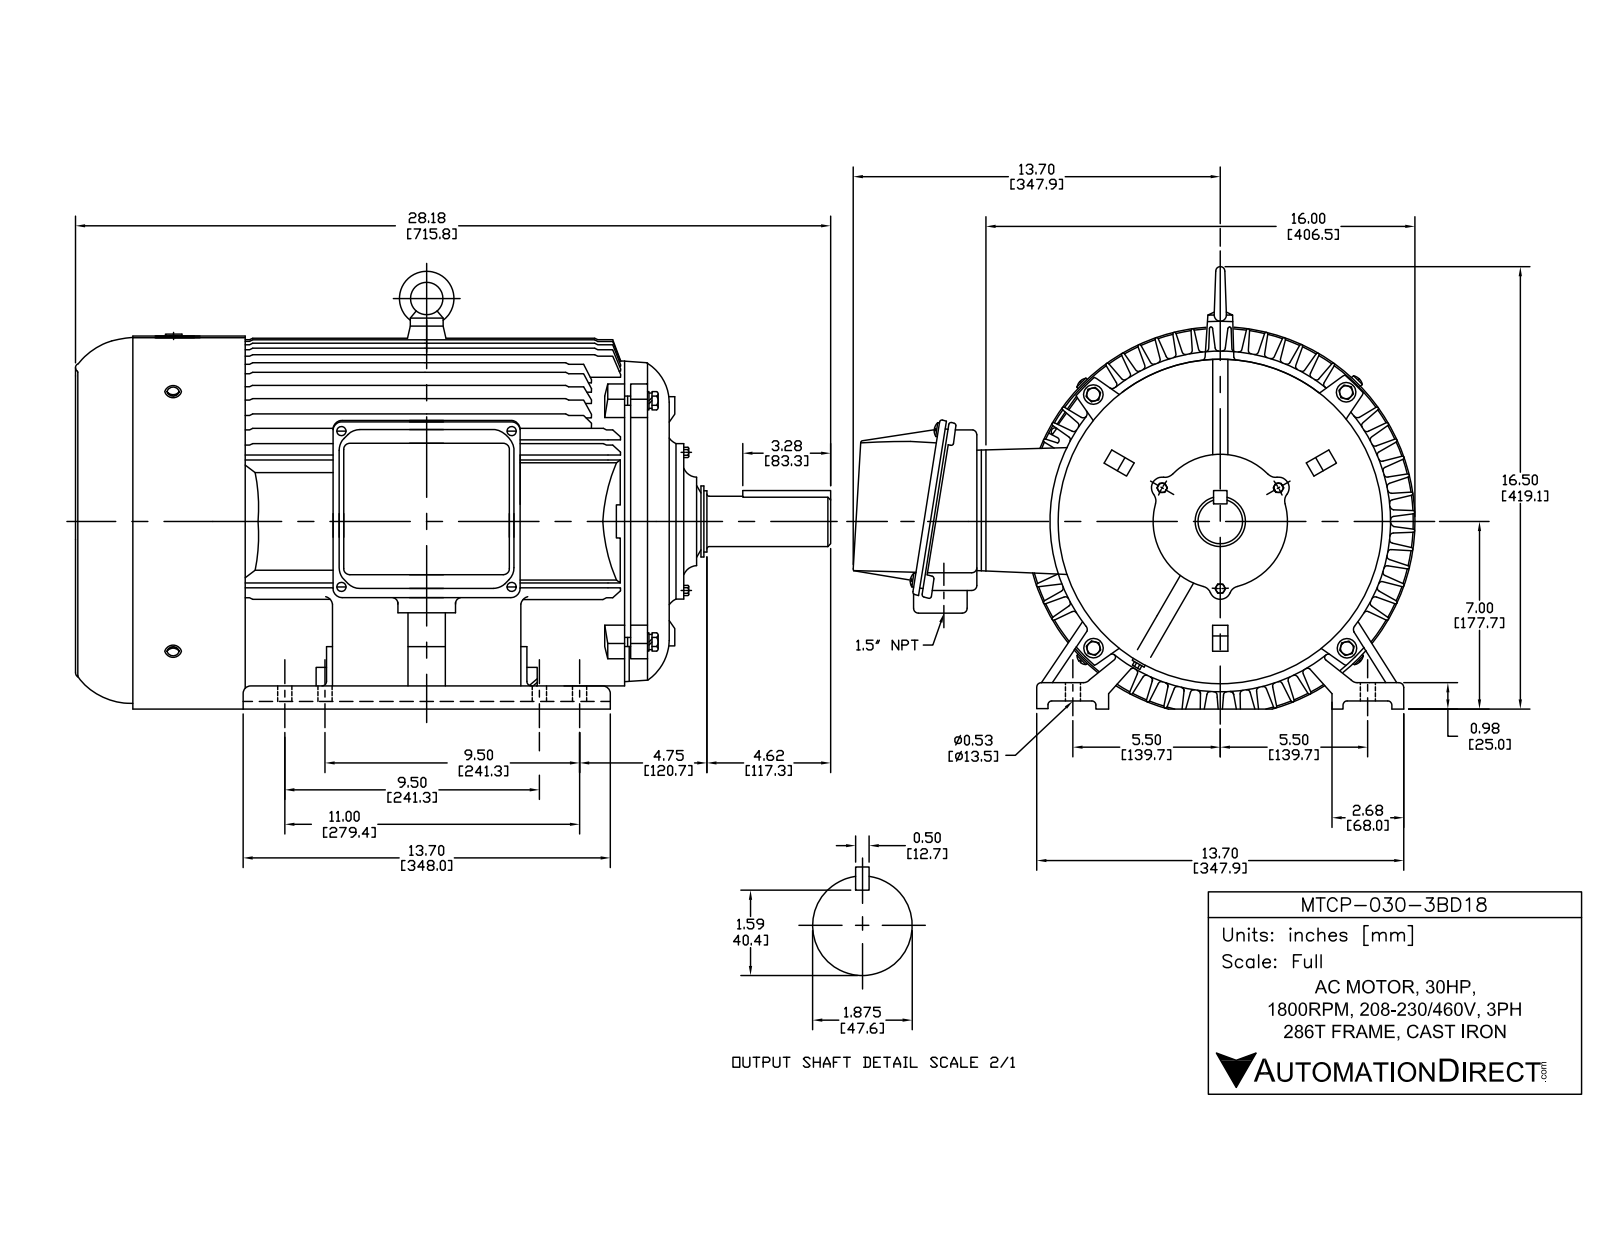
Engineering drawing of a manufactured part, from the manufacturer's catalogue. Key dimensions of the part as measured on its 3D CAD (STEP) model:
Part name (STEP PRODUCT): hexagon head bolts-full thread gb_GB_FASTENER_BOLT_STBAB A M8X50-N; hexagon head bolts-full thread gb_GB_FASTENER_BOLT_STBAB A M12X45-N; MTCP286T; eyebolts gb_GB_FASTENER_SCREWS_FRS M16-N (+8 more)
STEP written by: SolidWorks 2017 (AUTOMOTIVE_DESIGN)
Units: millimetres
Bodies: 68 solids, 3885 faces (1109 planar, 1437 cylindrical, 1339 other)
Overall size (bounding box): 719.5 × 489.93 × 443
Volume: 11 390 000 mm³ · Surface area: 3 171 000 mm²
Round holes (diameter × count): ⌀7 ×14, ⌀10 ×10, ⌀5 ×8, ⌀17 ×8, ⌀6.4 ×4, ⌀6.68 ×4, ⌀6.8 ×4, ⌀8.5 ×4, ⌀9 ×4, ⌀10.2 ×4, ⌀11.39 ×4, ⌀12.9 ×4
Round bosses / shafts (diameter × count): ⌀12 ×8, ⌀6 ×8, ⌀8 ×6, ⌀24 ×4, ⌀19.1 ×4, ⌀9.88 ×4, ⌀5 ×4, ⌀10 ×2
Partial cylindrical surfaces — rounded edges, fillets, slot ends (radius × count): R1 ×265, R5 ×78, R3 ×76, R0.5 ×48, R1.5 ×36, R0.75 ×24, R10 ×24, R8 ×18
Main face-to-face distances: 1.5, 5, 20, 40, 558.5, 557, 8.5, 567, 565.5, 13
Hole centre spacings: 144, 100, 65, 70, 116.94, 213.78, 67.64, 5
